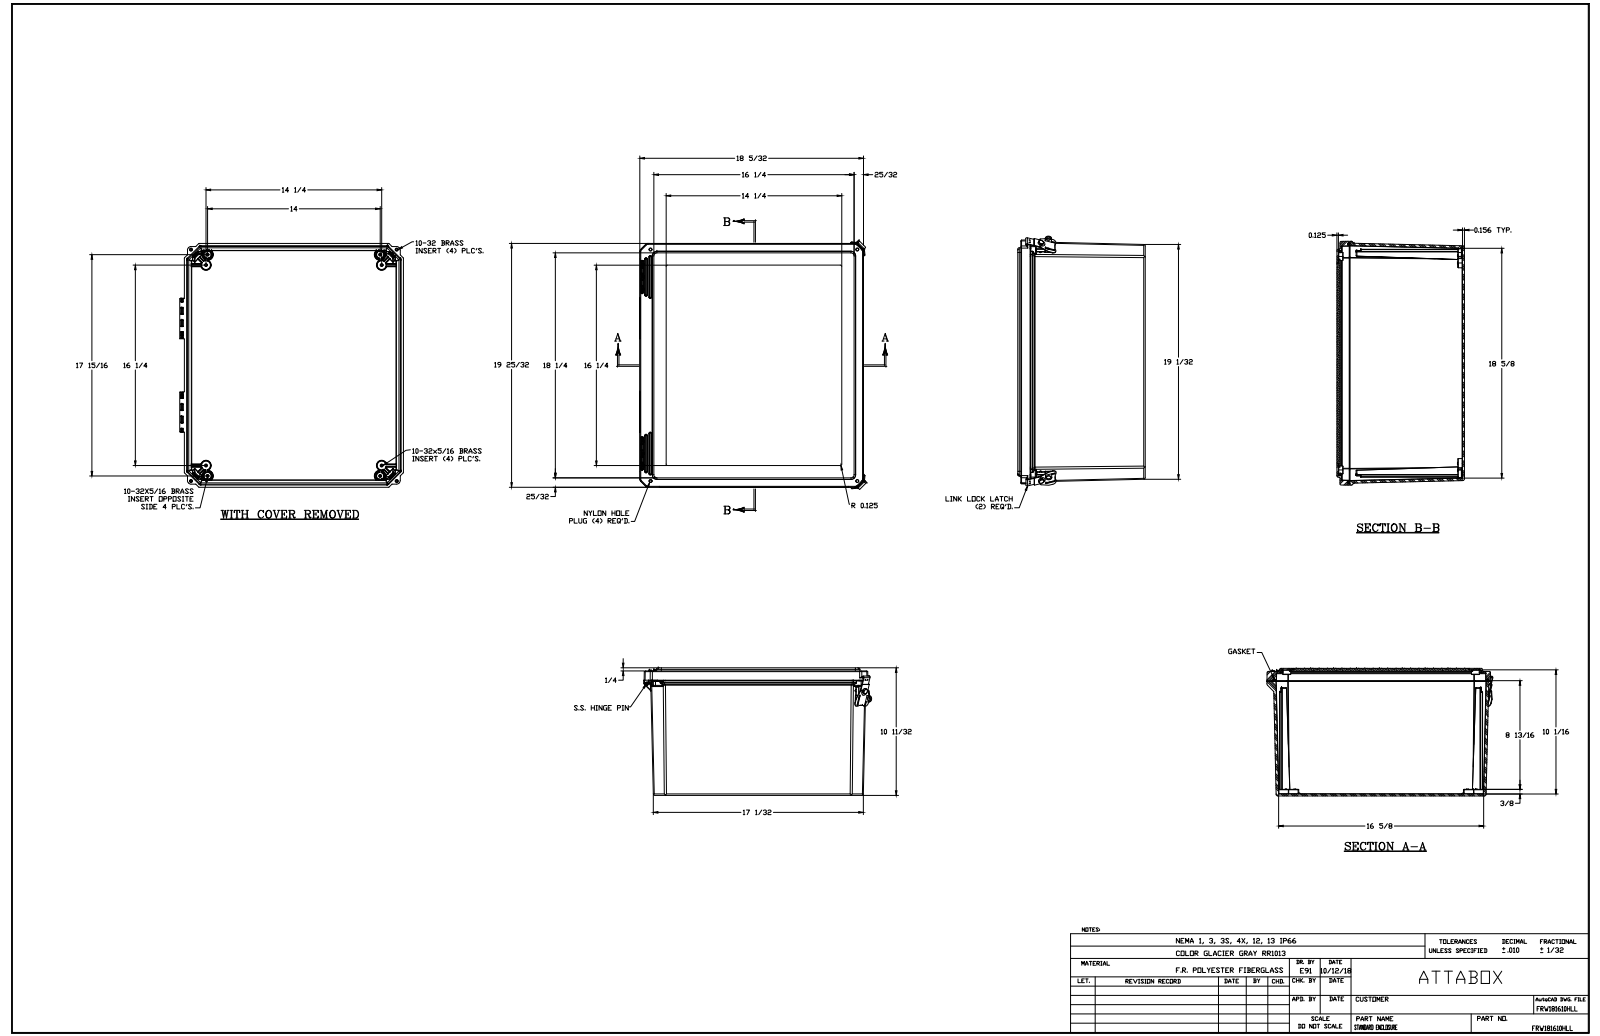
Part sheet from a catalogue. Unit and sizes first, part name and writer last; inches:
Units: inches
Overall size (bounding box): 20.565 × 18.547 × 10.344
Round holes (diameter × count): ⌀0.156 ×16, ⌀0.152 ×8, ⌀0.15 ×4, ⌀0.252 ×4, ⌀0.253 ×4, ⌀0.05 ×2, ⌀0.098 ×2, ⌀0.12 ×2, ⌀0.137 ×2, ⌀0.219 ×2, ⌀0.227 ×2, ⌀0.313 ×2
Round bosses / shafts (diameter × count): ⌀0.246 ×16, ⌀0.209 ×4, ⌀0.6 ×2, ⌀0.435 ×2, ⌀0.2 ×2, ⌀0.135 ×2, ⌀0.05 ×2, ⌀0.135 ×1
Partial cylindrical surfaces — rounded edges, fillets, slot ends (radius × count): R0.01 ×190, R0.005 ×88, R0.02 ×49, R0.125 ×38, R0.03 ×37, R0.039 ×28, R0.03 ×24, R0.09 ×24
Main face-to-face distances: 0.156, 0.202, 0.2, 10.119, 9.963, 10.344, 10.188, 0.225, 0.125, 0.25
Hole centre spacings: 1.783, 14.15, 15.562, 17.556, 17.555, 18.409, 21.613, 23.392
Volume: 283.2 in³ · Surface area: 3 035 in²
Bodies: 38 solids, 2363 faces (835 planar, 924 cylindrical, 604 other)
Part name (STEP PRODUCT): FRW181610HLL
STEP written by: SolidWorks 2018 (AUTOMOTIVE_DESIGN)
